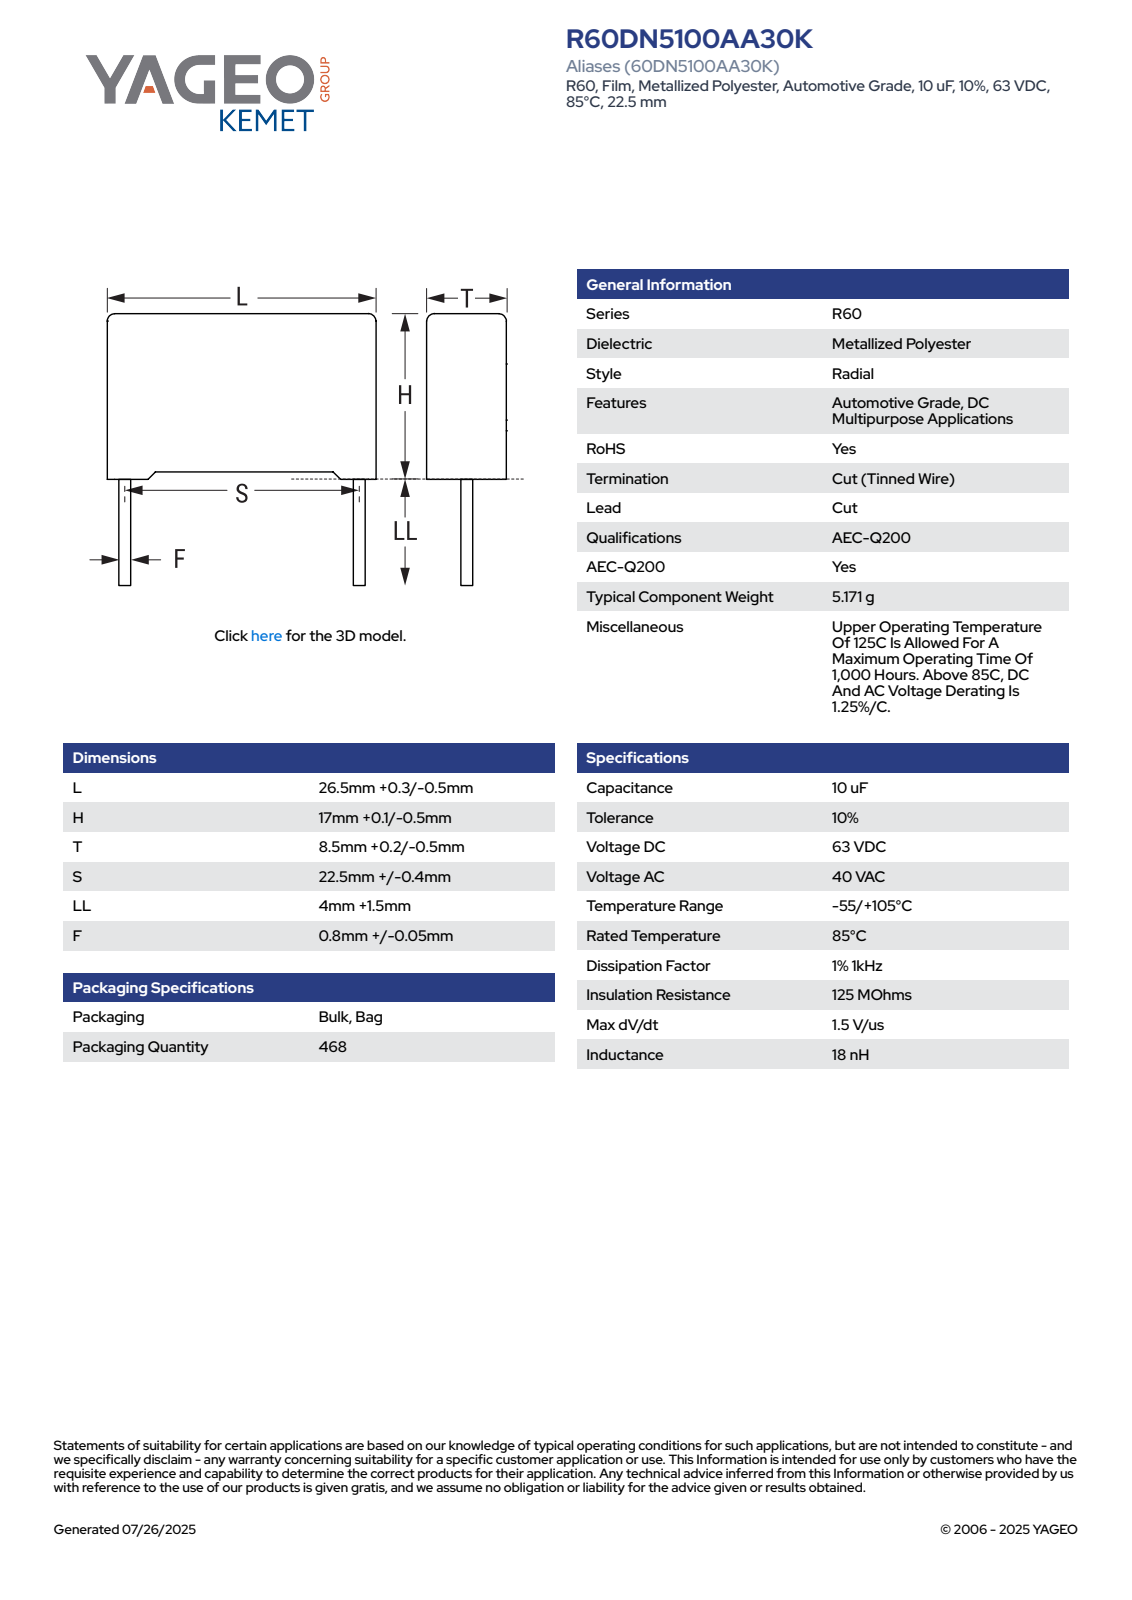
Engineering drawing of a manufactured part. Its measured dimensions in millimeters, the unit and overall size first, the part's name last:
Units: millimetres
Overall size (bounding box): 26.8 × 22.6 × 8.71
Round bosses / shafts (diameter × count): ⌀0.85 ×2
Partial cylindrical surfaces — rounded edges, fillets, slot ends (radius × count): R0.5 ×4
Main face-to-face distances: 8.7, 16.35, 26.8, 16.51, 0.89, 0.75, 0.59, 17.1, 7.81, 8.71
Volume: 3 841 mm³ · Surface area: 1 757 mm²
Bodies: 4 solids, 85 faces (77 planar, 8 cylindrical, 0 other)
Part name (STEP PRODUCT): CFR_RB2_26.5X17X8.5_L26.8H17.1T8.7S22.5LL5.5F0.85
STEP written by: SolidWorks 2021 (AUTOMOTIVE_DESIGN)
